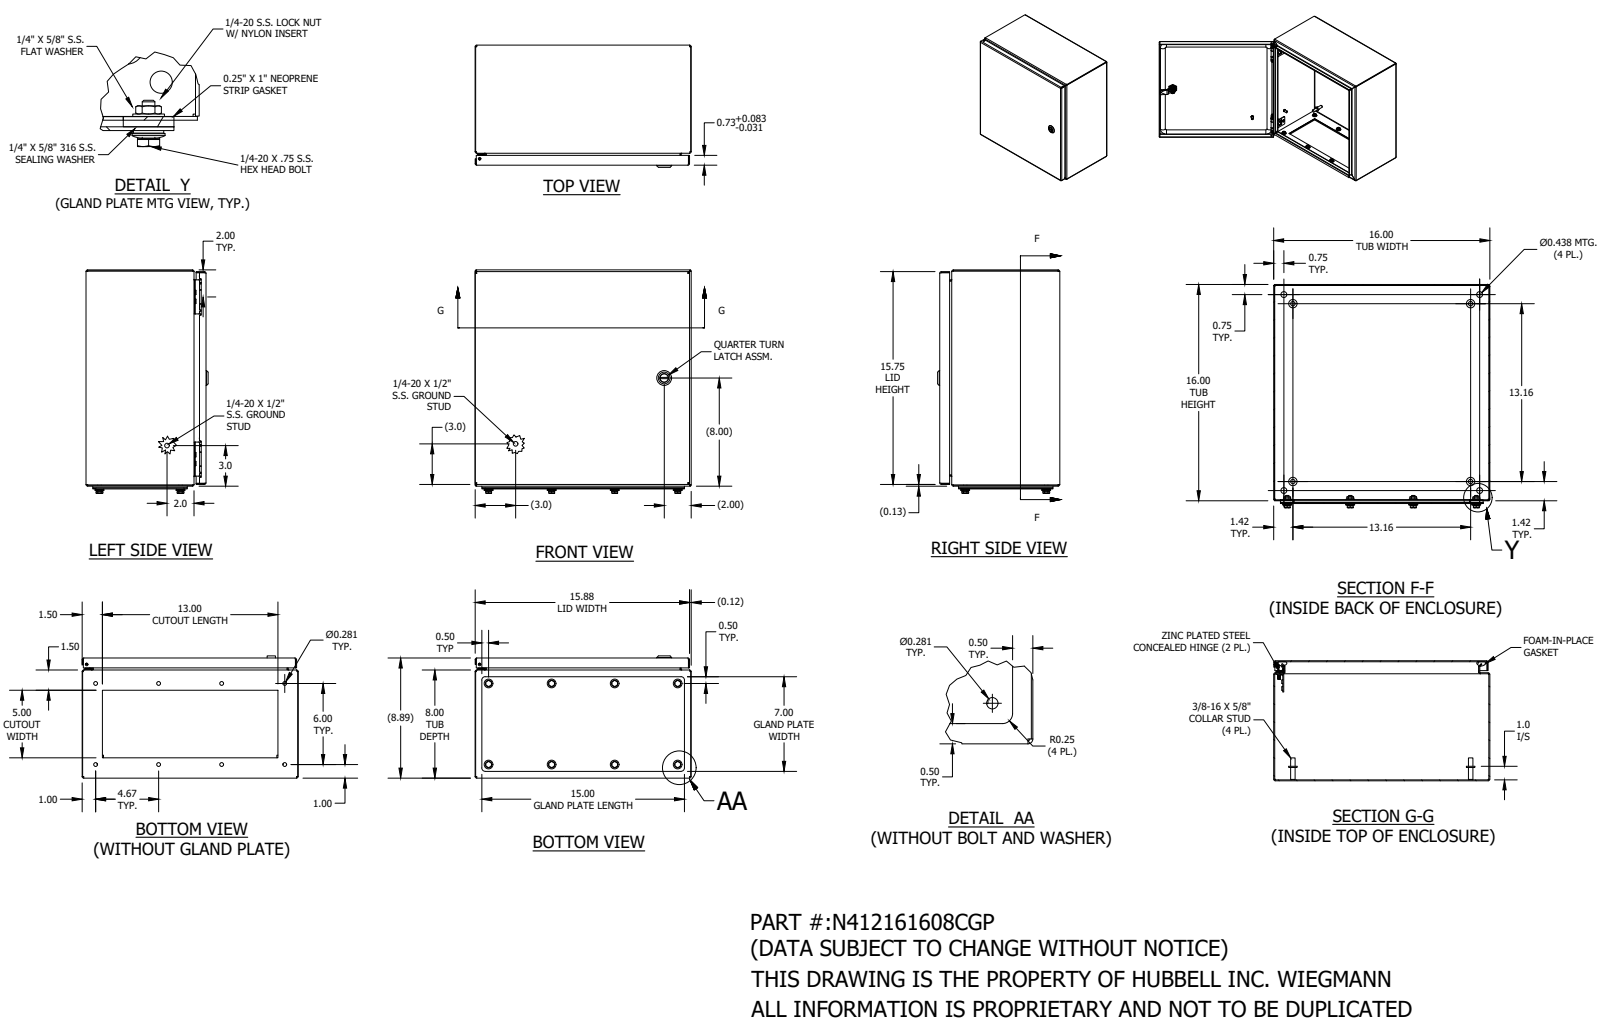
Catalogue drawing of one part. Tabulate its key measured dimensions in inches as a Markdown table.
| quantity | value |
| --- | --- |
| part name | N412161608CGP |
| STEP written by | SolidWorks 2019 (AUTOMOTIVE_DESIGN) |
| units | inches |
| bodies | 71 solids, 2035 faces (794 planar, 624 cylindrical, 617 other) |
| overall size | 16.519 × 16 × 9.044 |
| volume | 107.7 in³ |
| surface area | 2 641 in² |
| round holes (diameter × count) | 0.16 × 8, 0.211 × 8, 0.281 × 8, 0.29 × 8, 0.35 × 6, 0.188 × 5, 0.093 × 4, 0.167 × 4, 0.235 × 4, 0.235 × 4, 0.275 × 4, 0.275 × 4 |
| round bosses / shafts (diameter × count) | 0.25 × 18, 0.65 × 8, 0.6 × 8, 0.438 × 8, 0.625 × 7, 0.625 × 5, 0.36 × 4, 0.33 × 4 |
| partial cylindrical surfaces (radius × count) | 0.012 × 30, 0.05 × 26, 0.047 × 20, 0.121 × 20, 0.02 × 13, 0.125 × 8, 0.13 × 8, 0.157 × 5 |
| main face-to-face distances | 0.074, 8.812, 8.738, 8.886, 16.13, 15.926, 15.852, 0.074, 15.926, 16 |
| hole center spacings | 7.601, 6, 4.667, 12.004, 14.5, 0.658, 0.66, 4.667 |
